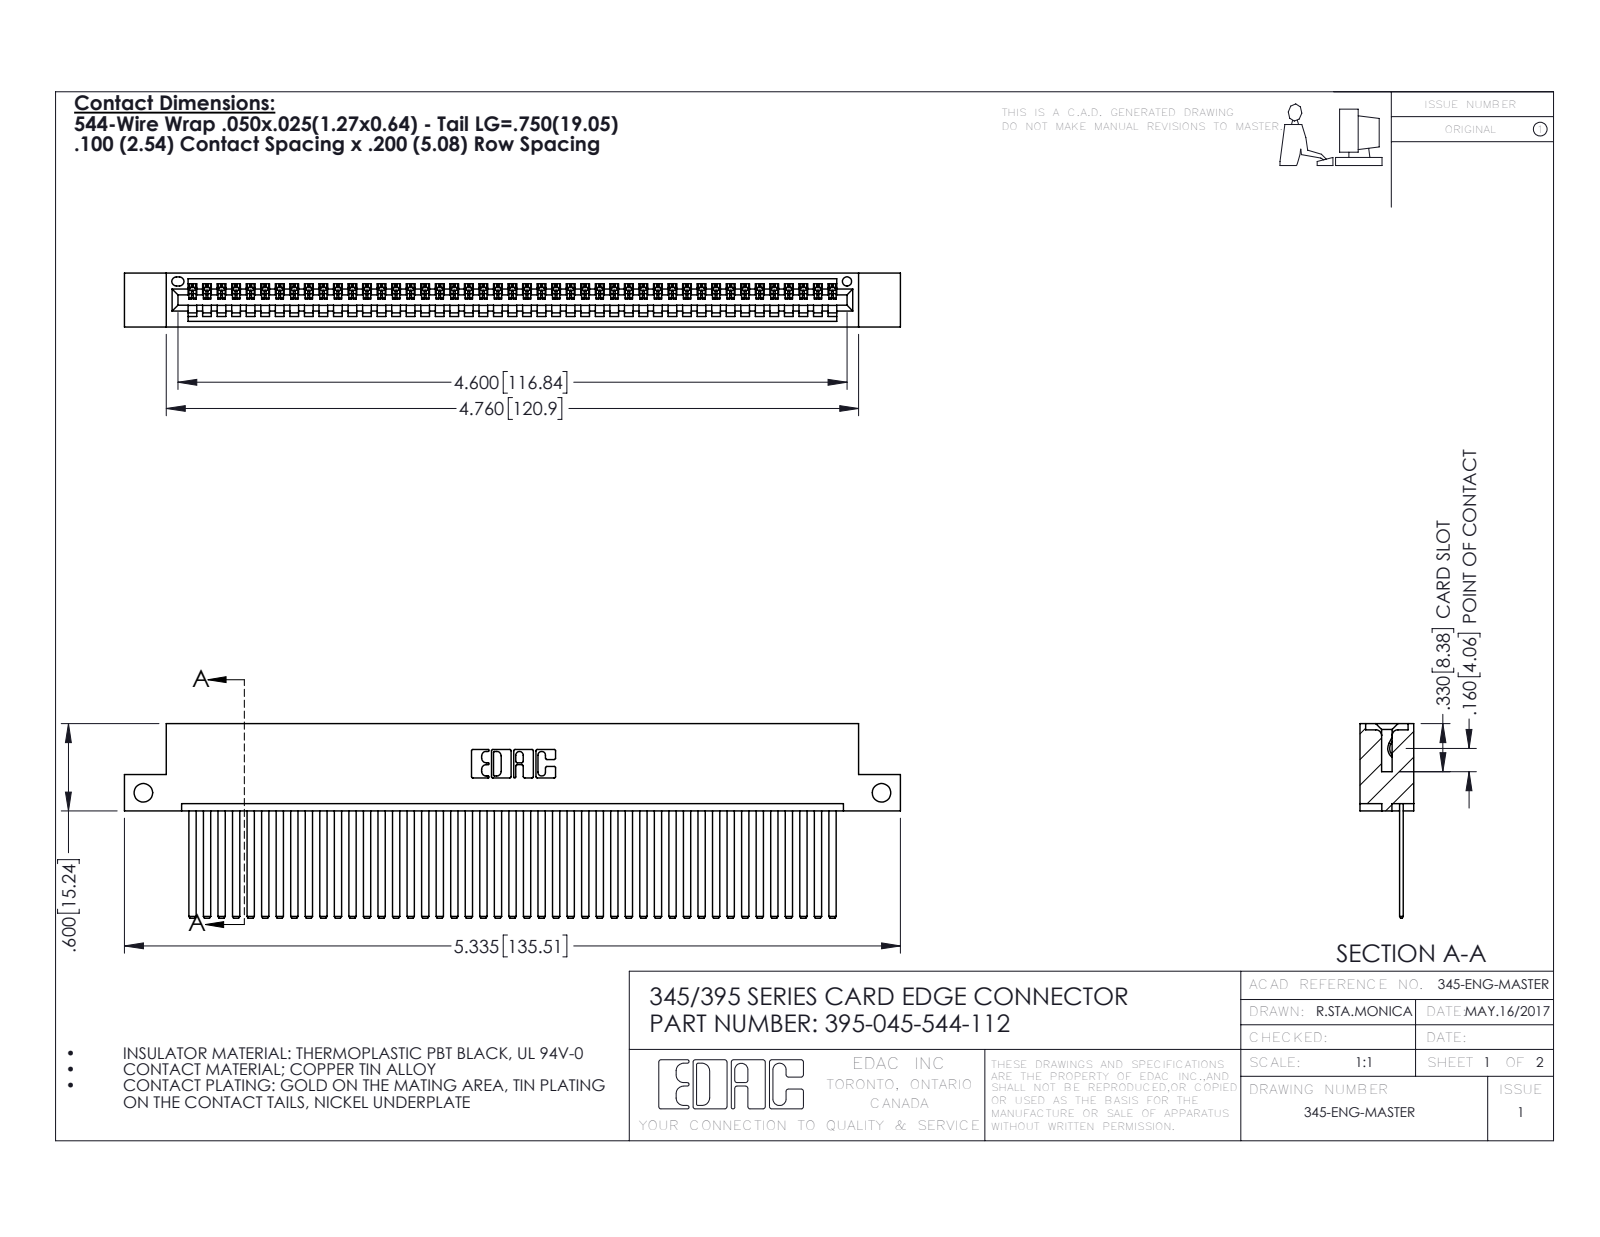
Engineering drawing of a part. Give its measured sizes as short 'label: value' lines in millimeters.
name: 345 Part_Flush Mounting Lugs - Side Mount; 345-292-001_345-293-144; 395-045-544-112
written by: SolidWorks 2016 (CONFIG_CONTROL_DESIGN)
unit: mm
bodies: 46 solids, 2466 faces (1700 planar, 766 cylindrical, 0 other)
size: 135.5 × 34 × 9.4
volume: 13 300 mm³; area: 19 170 mm²
holes: 2× ⌀3.3, 1× ⌀1.6
rounds: 90× R0.2, 22× R0.3, 6× R0.2, 6× R0.8, 3× R0.7, 2× R0.8, 2× R1, 1× R0.4
face distances: 1.8, 7.6, 0.6, 2.5, 6.9, 9.4, 5.1, 5.7, 3.8, 1.8
hole spacings: 128.9
